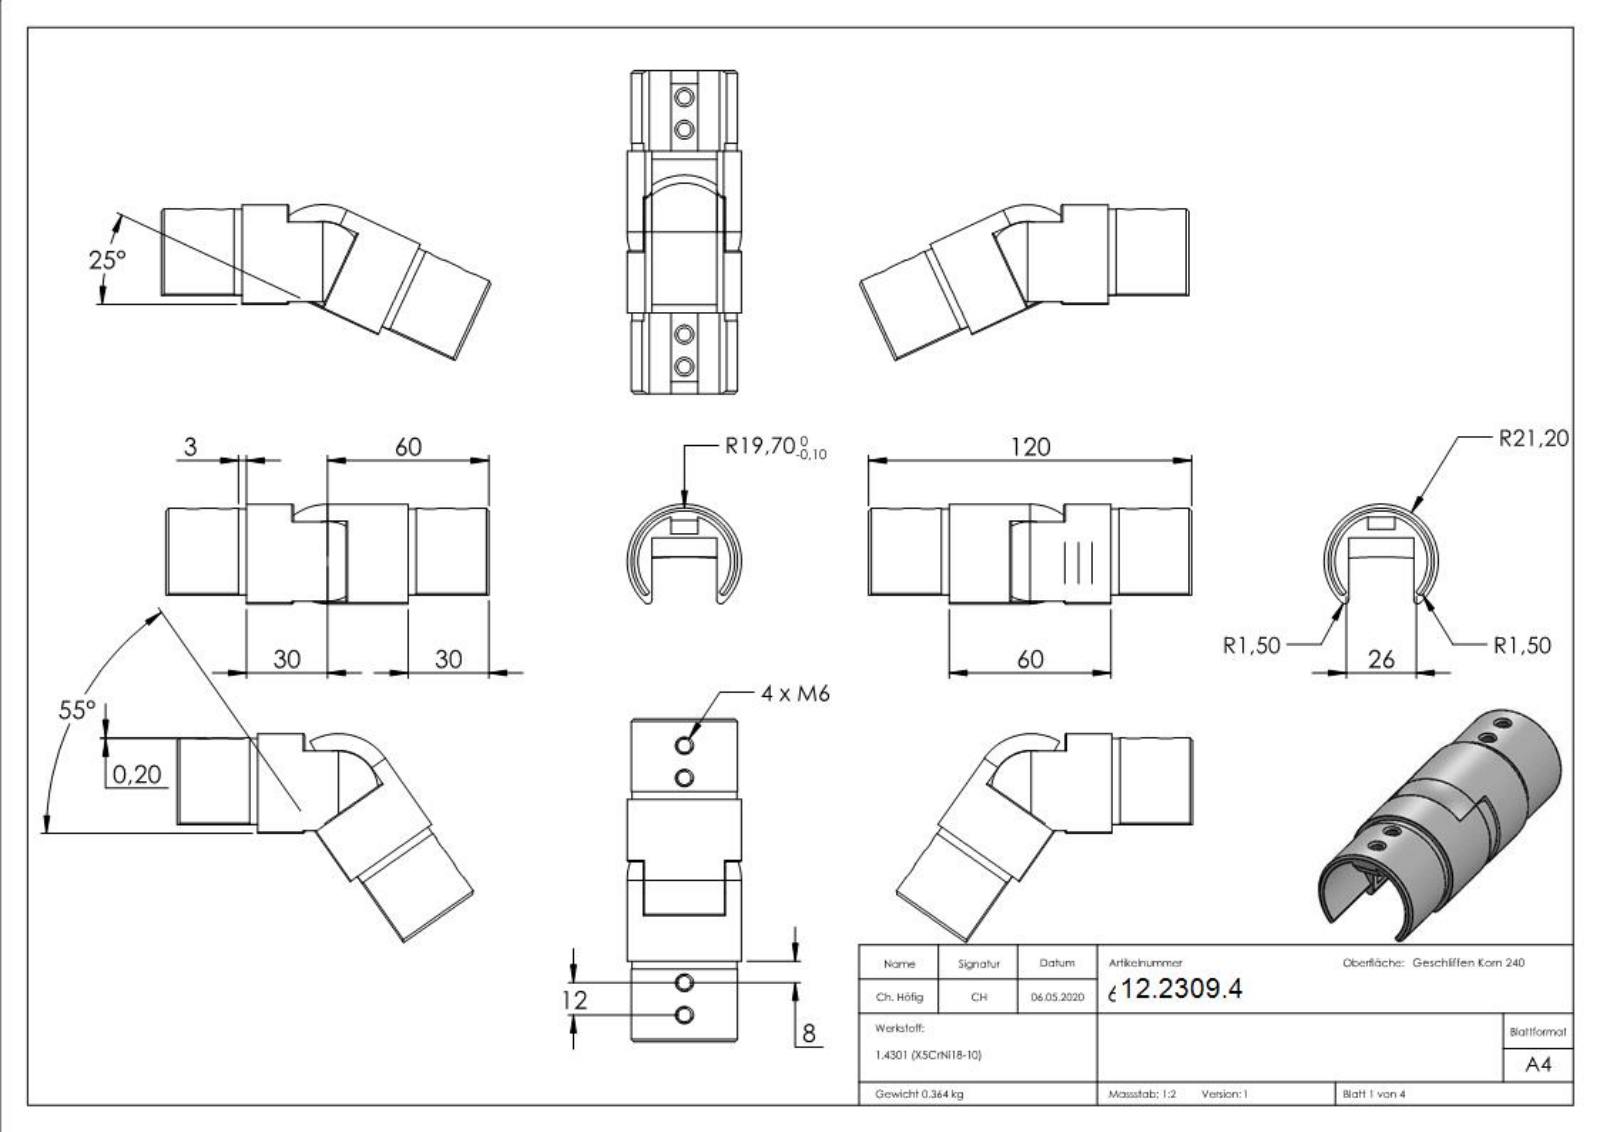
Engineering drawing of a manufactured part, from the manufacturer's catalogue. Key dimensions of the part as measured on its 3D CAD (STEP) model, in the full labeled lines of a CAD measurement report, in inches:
Part name (STEP PRODUCT): 60314-240 Teil2_60314-240 Teil2; 60314-240 Teil1_60314-240 Teil1; 60314-240
STEP written by: SolidWorks 2015 (CONFIG_CONTROL_DESIGN)
Units: inches
Bodies: 2 solids, 313 faces (156 planar, 30 cylindrical, 127 other)
Overall size (bounding box): 4.724 × 1.669 × 1.457
Volume: 2.835 in³ · Surface area: 45.39 in²
Round holes (diameter × count): ⌀0.197 ×4, ⌀0.394 ×1
Round bosses / shafts (diameter × count): ⌀0.354 ×1
Partial cylindrical surfaces — rounded edges, fillets, slot ends (radius × count): R0.059 ×4, R0.677 ×1, R0.719 ×1, R0.768 ×1, R0.776 ×1, R0.835 ×1
Main face-to-face distances: 0.124, 1.073, 1.189, 0.116, 1.065, 0.949, 1.181, 1.197, 0.394, 0.402
Hole centre spacings: 0.472, 3.465, 2.992, 3.937
